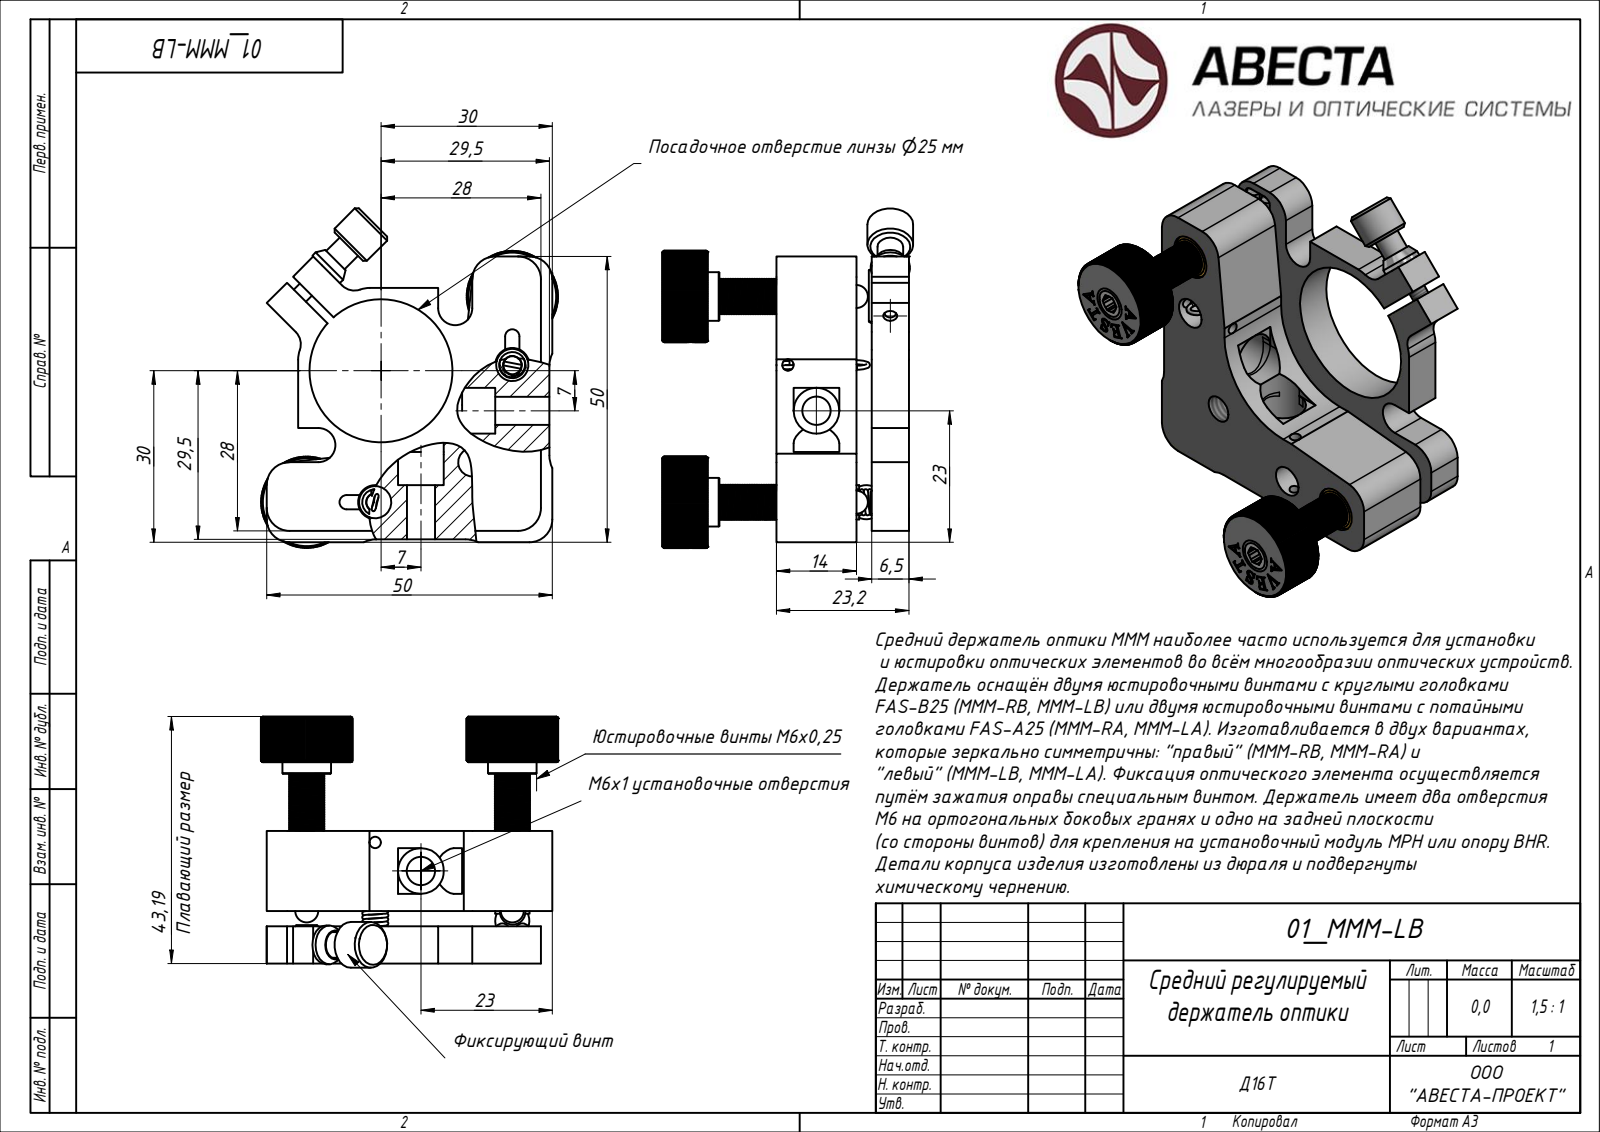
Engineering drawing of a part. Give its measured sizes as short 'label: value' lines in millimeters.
written by: ST-DEVELOPER v15 (AUTOMOTIVE_DESIGN)
unit: mm
bodies: 17 solids, 684 faces (317 planar, 0 cylindrical, 367 other)
size: 59.41 × 52 × 41.45
volume: 28 879 mm³; area: 18 217 mm²
face distances: 6.5, 14, 9.98, 17.48, 23.98, 3.48, 2, 1.5, 0.5, 8
